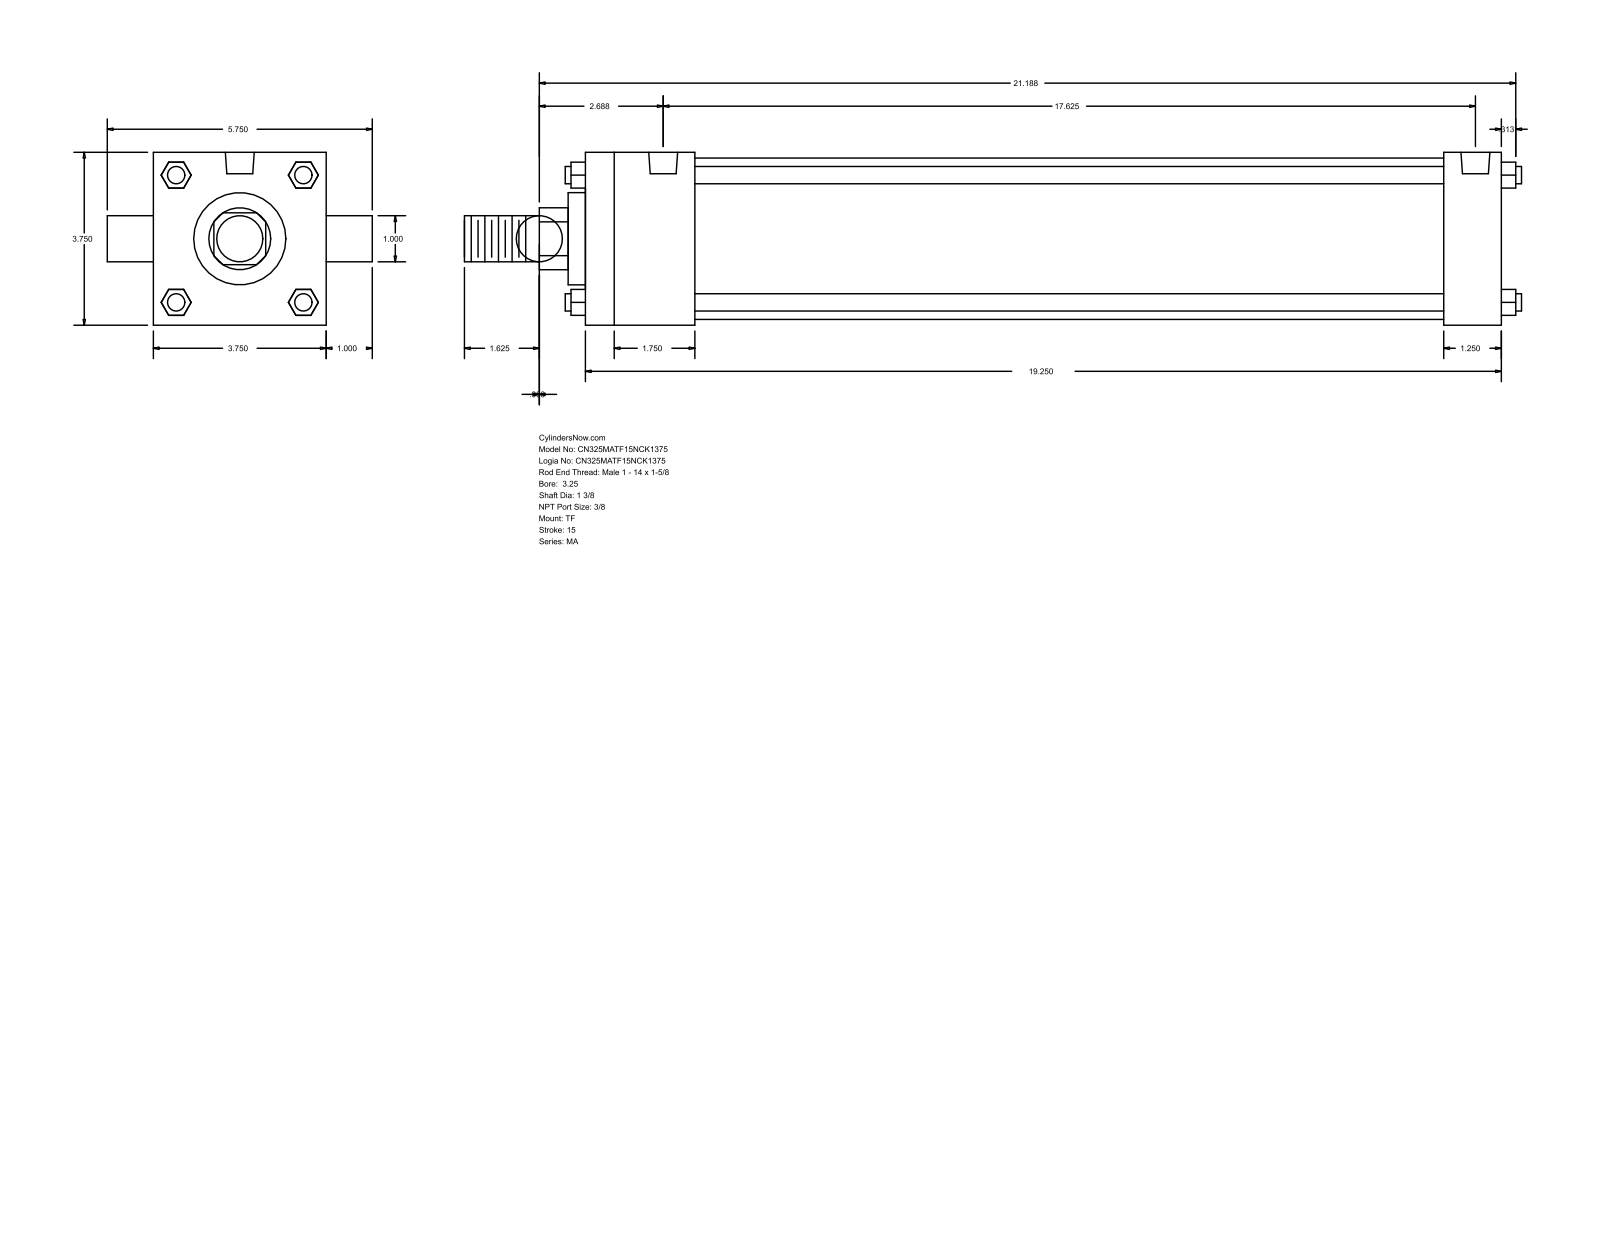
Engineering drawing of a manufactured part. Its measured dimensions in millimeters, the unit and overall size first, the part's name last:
Units: millimetres
Overall size (bounding box): 582.61 × 146.05 × 95.25
Round holes (diameter × count): ⌀11.11 ×3, ⌀15.93 ×2
Round bosses / shafts (diameter × count): ⌀9.53 ×4, ⌀25.4 ×2, ⌀88.9 ×1, ⌀50.8 ×1, ⌀34.92 ×1
Partial cylindrical surfaces — rounded edges, fillets, slot ends (radius × count): R17.06 ×1
Main face-to-face distances: 95.24, 504.83, 60.32, 473.08, 412.76, 444.51, 31.75, 9.52, 69.84, 482.6
Hole centre spacings: 4.76, 4.77, 438.15, 442.91, 442.92, 447.68
Bodies: 0 solids, 120 faces (92 planar, 28 cylindrical, 0 other)
Part name (STEP PRODUCT): MA_TF__0325_1.375
STEP written by: GSSL Pune (CONFIG_CONTROL_DESIGN)
